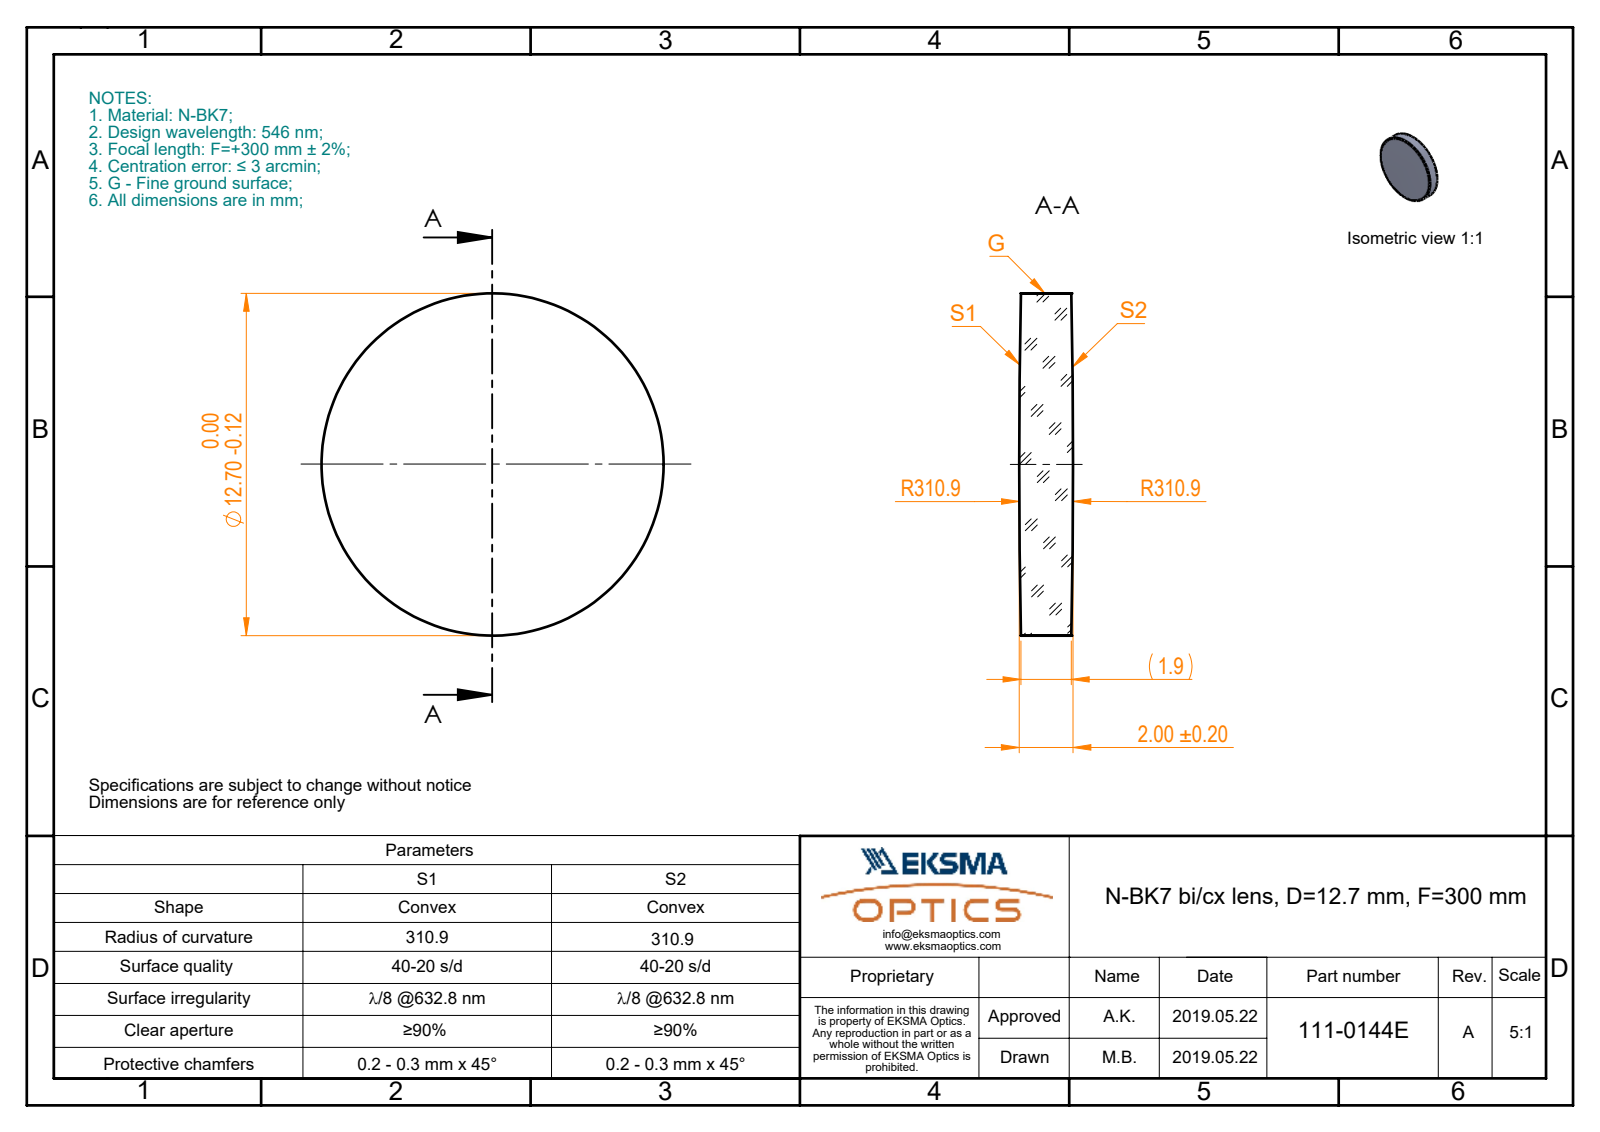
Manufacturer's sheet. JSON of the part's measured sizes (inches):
{"part_name": "111-0144E BK7 bi-cx 12.7 F300", "step_written_by": "SolidWorks 2017 (CONFIG_CONTROL_DESIGN)", "units": "inches", "bodies": {"solids": 1, "faces": 6, "planar": 0, "cylindrical": 2, "other": 4}, "overall_size": [0.5, 0.5, 0.079], "volume_in3": 0.015, "surface_area_in2": 0.508, "round_bosses_or_shafts": [[0.5, 1]]}
